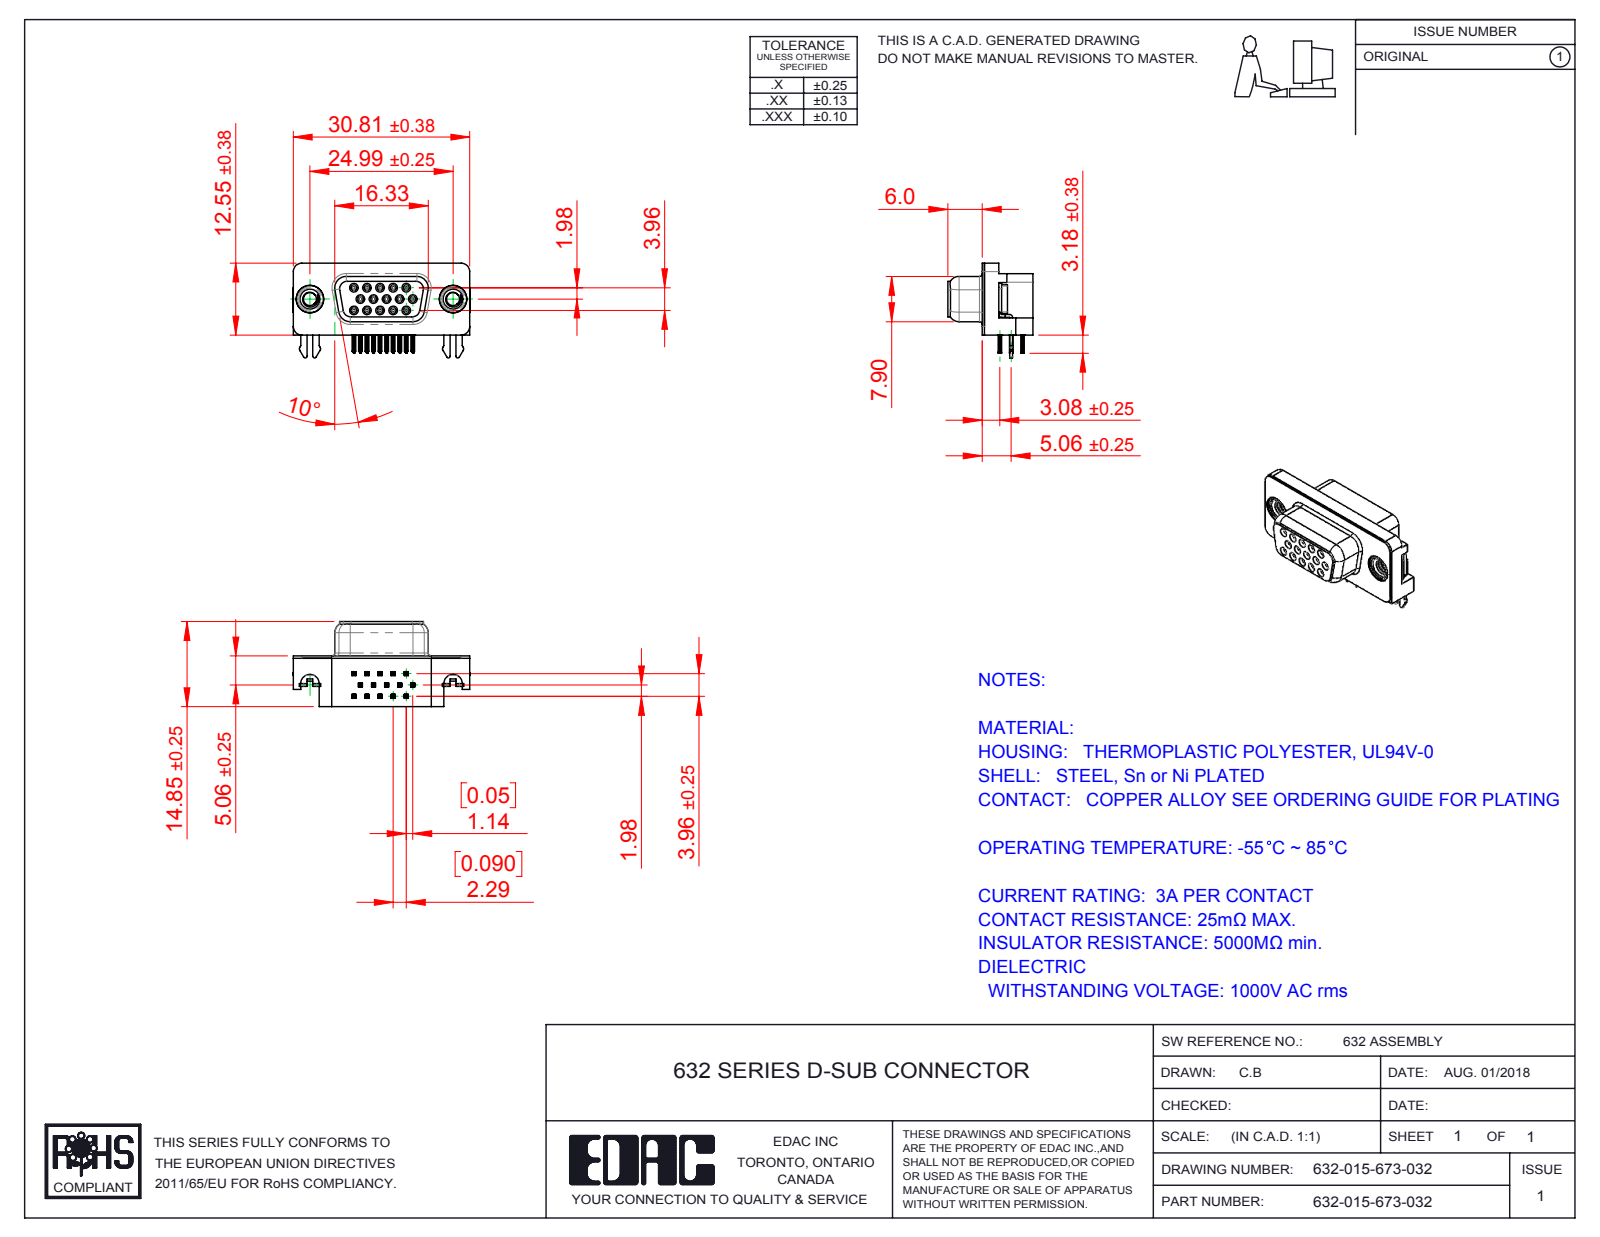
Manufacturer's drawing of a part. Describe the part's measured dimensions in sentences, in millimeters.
The part is named "632 Contact Top; 632 Housing_15 Socket; 632 Shell_9 Socket; 632 Contact Middle_Recessed (+5 more)". Its 3-D file was written by "SolidWorks 2016 (CONFIG_CONTROL_DESIGN)". It is 21 solids with 2338 faces: 990 planar, 612 cylindrical and 736 other. Overall it measures 30.89 by 16.55 by 14.85 millimeters. Its volume is 2 921 cubic millimeters and its surface area 5 015 square millimeters. Round holes: 15 of diameter 0.8, 15 of diameter 0.9, 2 of diameter 2.26, 2 of diameter 4, 2 of diameter 4.8, 2 of diameter 5. Round bosses or shafts: 15 of diameter 1.2, 2 of diameter 4.9, 2 of diameter 4.75, 2 of diameter 3.9. Partial cylindrical surfaces (rounded edges, fillets, slot ends): 120 of radius 0.1, 60 of radius 0.15, 30 of radius 0.35, 15 of radius 0.34, 11 of radius 1, 10 of radius 0.28, 10 of radius 0.5, 8 of radius 0.25. The main face-to-face distances are 0.4, 1.98, 8.45, 8.85, 2.9, 2.5, 5.95, 6.4, 6.7, 7.05. The hole center spacings are 2.28, 2.29, 3.96, 4.57, 6.05, 3.97, 4.58, 6.86.
